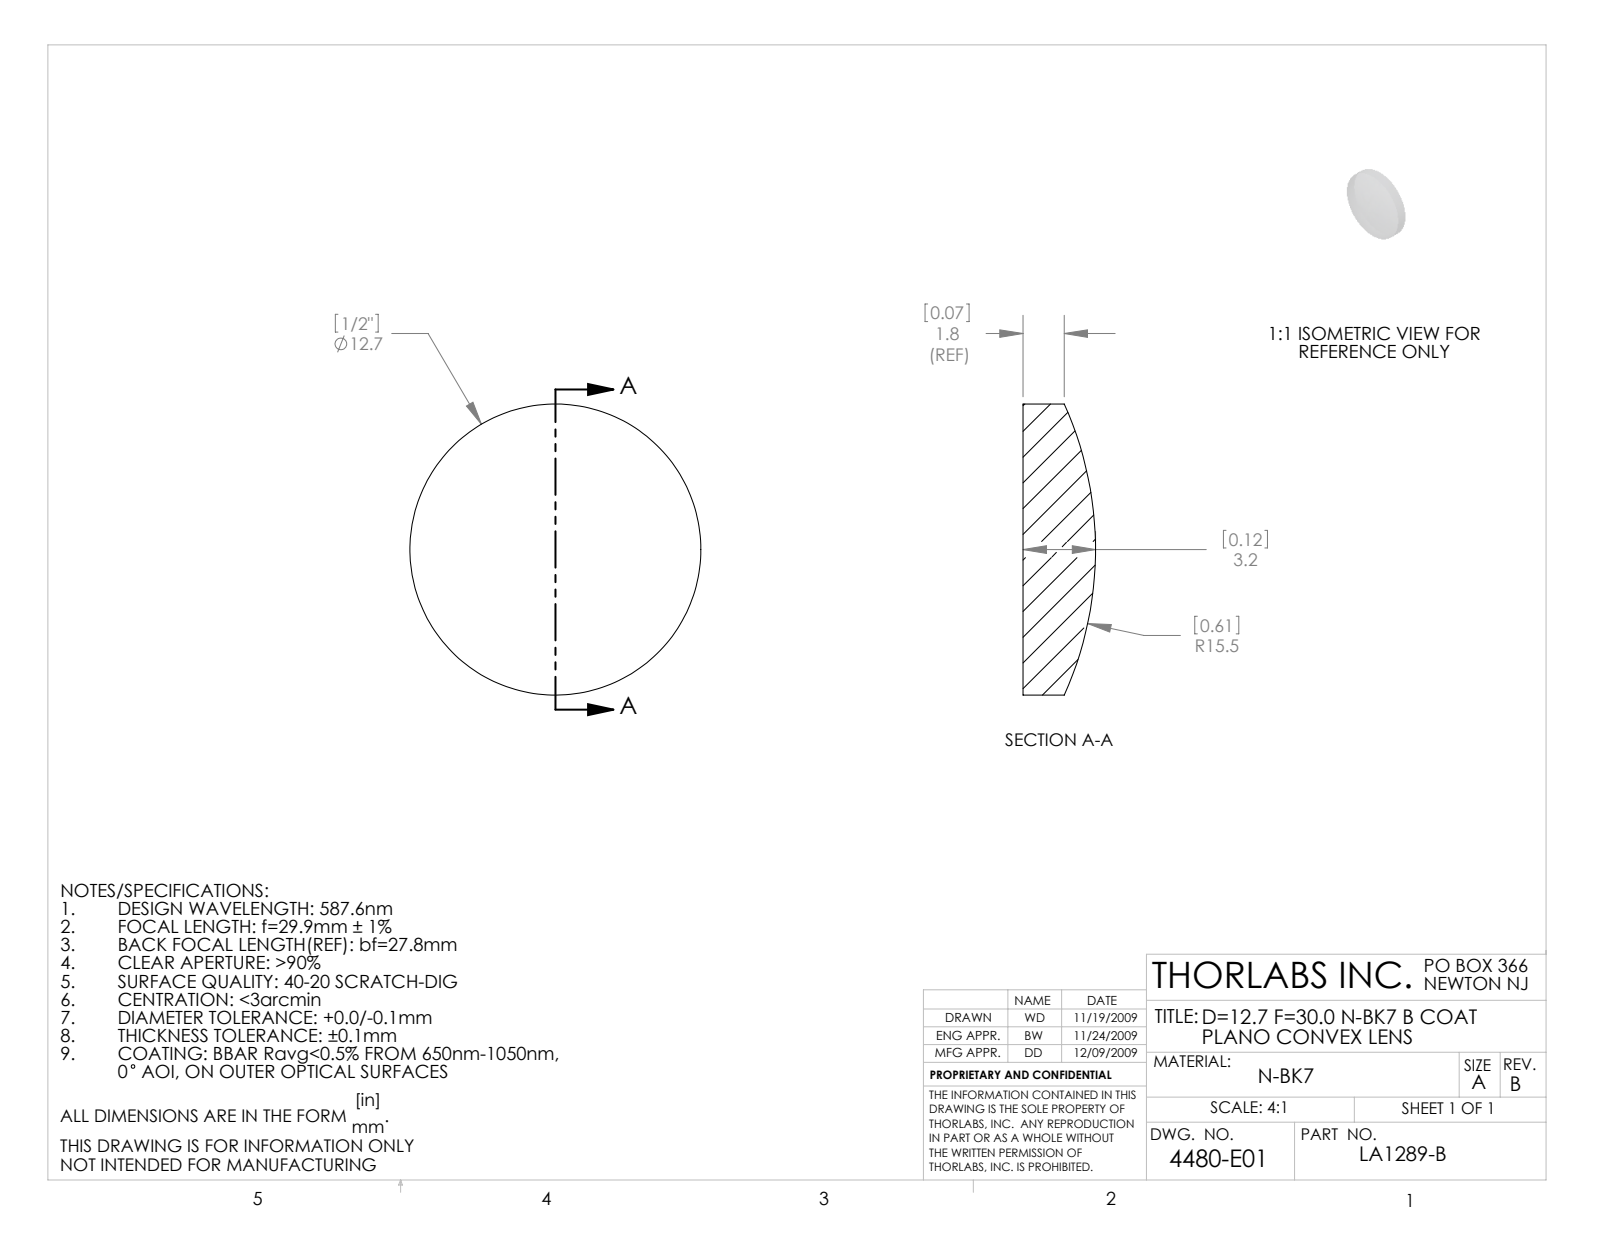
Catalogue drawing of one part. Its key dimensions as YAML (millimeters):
part_name: "4480-E0W"
step_written_by: "SolidWorks 2009 (AUTOMOTIVE_DESIGN)"
units: millimeters
bodies: {solids: 1, faces: 5, planar: 1, cylindrical: 2, other: 2}
overall_size: [12.7, 12.7, 3.16]
volume: 315
surface_area: 331
round_bosses_or_shafts:
  - {diameter: 12.7, count: 1}
